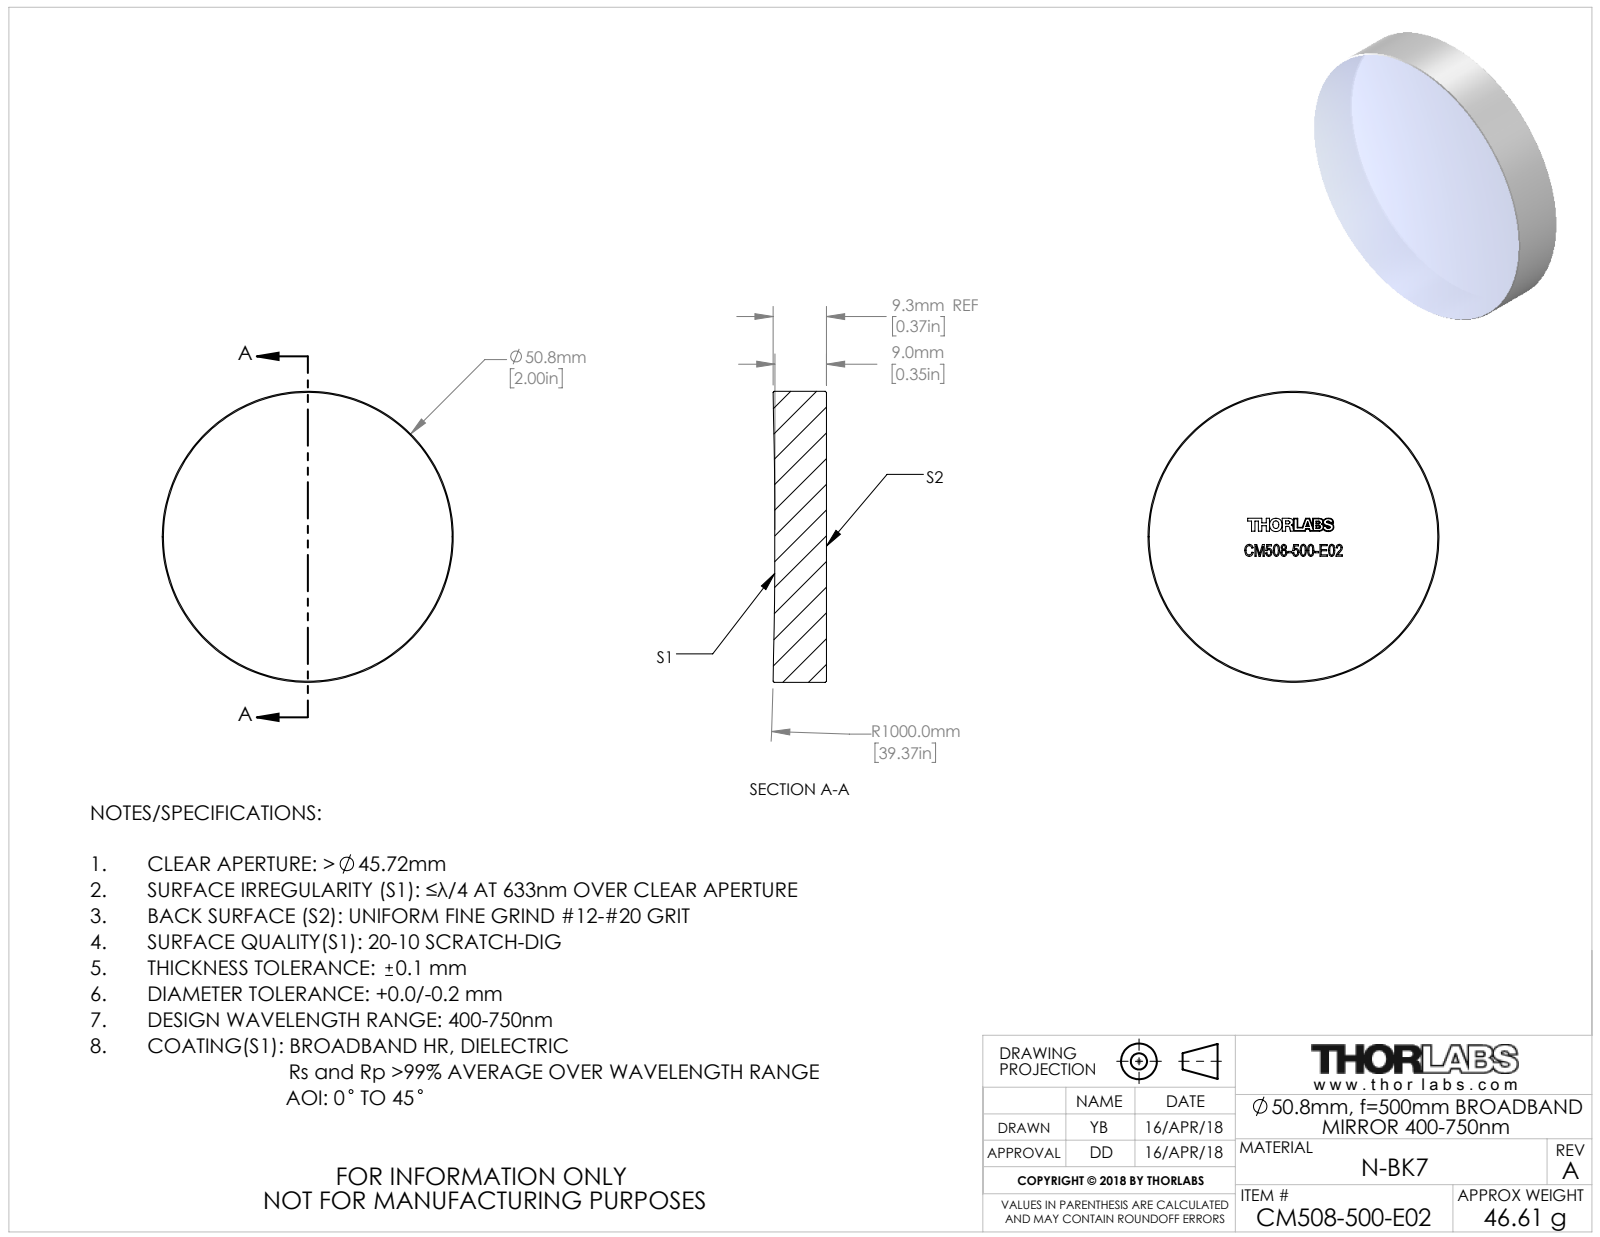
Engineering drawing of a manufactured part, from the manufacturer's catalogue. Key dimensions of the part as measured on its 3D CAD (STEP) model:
Part name (STEP PRODUCT): TTN153327-E0W
STEP written by: SolidWorks 2018 (CONFIG_CONTROL_DESIGN)
Units: millimetres
Bodies: 1 solid, 43 faces (35 planar, 2 cylindrical, 6 other)
Overall size (bounding box): 50.8 × 50.8 × 9.32
Volume: 18 562 mm³ · Surface area: 5 504 mm²
Round bosses / shafts (diameter × count): ⌀50.8 ×1
